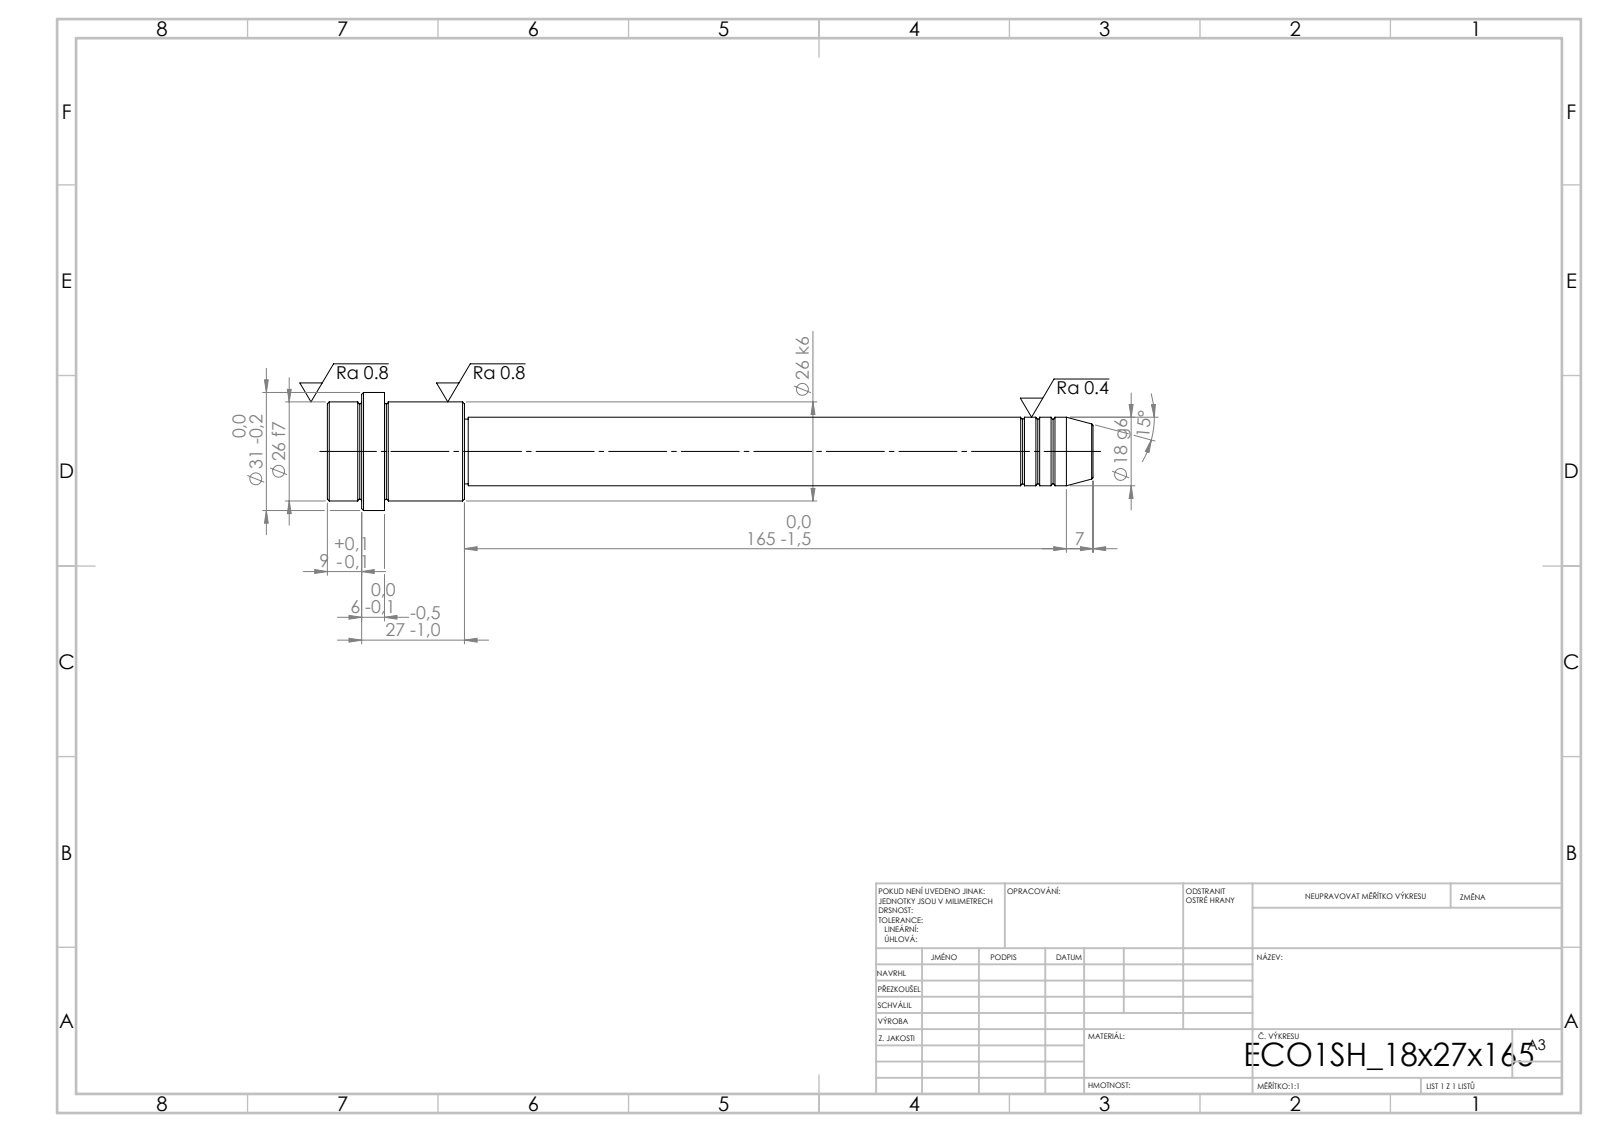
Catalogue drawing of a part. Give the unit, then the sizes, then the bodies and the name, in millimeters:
Units: millimetres
Overall size (bounding box): 201 × 31 × 31
Round bosses / shafts (diameter × count): ⌀31 ×1, ⌀26 ×1, ⌀18 ×1, ⌀17 ×1
Main face-to-face distances: 36, 21, 15, 27, 6, 9, 165, 186, 192, 201
Volume: 61 909 mm³ · Surface area: 13 895 mm²
Bodies: 1 solid, 52 faces (6 planar, 16 cylindrical, 30 other)
STEP written by: SolidWorks 2019 (CONFIG_CONTROL_DESIGN)
